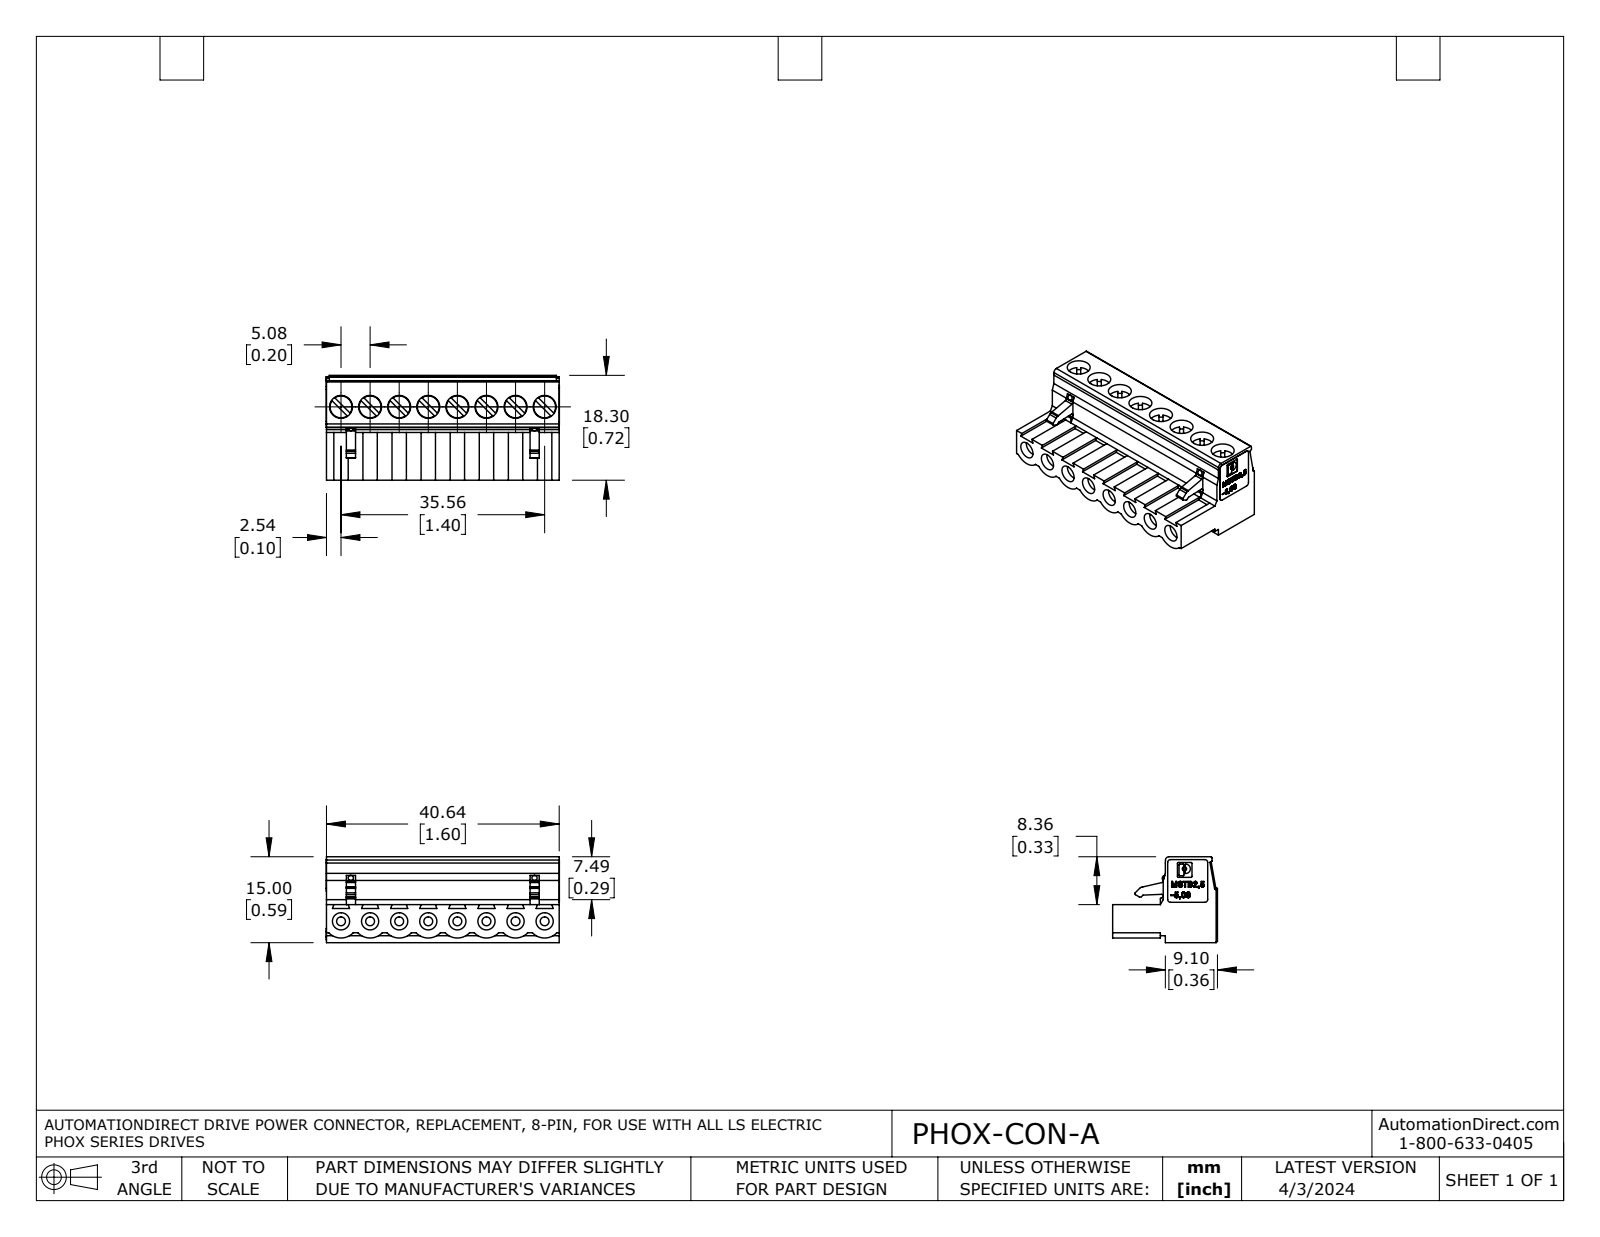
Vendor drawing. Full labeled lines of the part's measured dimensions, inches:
Part name (STEP PRODUCT): PHOX-CON-A
STEP written by: SolidWorks 2021 (AUTOMOTIVE_DESIGN)
Units: inches
Bodies: 1 solid, 986 faces (756 planar, 204 cylindrical, 26 other)
Overall size (bounding box): 1.602 × 0.72 × 0.591
Volume: 0.427 in³ · Surface area: 5.804 in²
Round holes (diameter × count): ⌀0.118 ×8, ⌀0.157 ×8
Round bosses / shafts (diameter × count): ⌀0.15 ×8, ⌀0.015 ×1
Partial cylindrical surfaces — rounded edges, fillets, slot ends (radius × count): R0.012 ×17, R0.02 ×12, R0.005 ×10, R0.102 ×8, R0.115 ×8, R0.008 ×5, R0.007 ×4, R0.015 ×1
Main face-to-face distances: 0.235, 0.591, 0.356, 0.261, 0.026, 0.329, 0.689, 0.031, 0.72, 0.373
Hole centre spacings: 0.2, 0.4, 0.6, 0.8, 1, 1.2, 1.4
